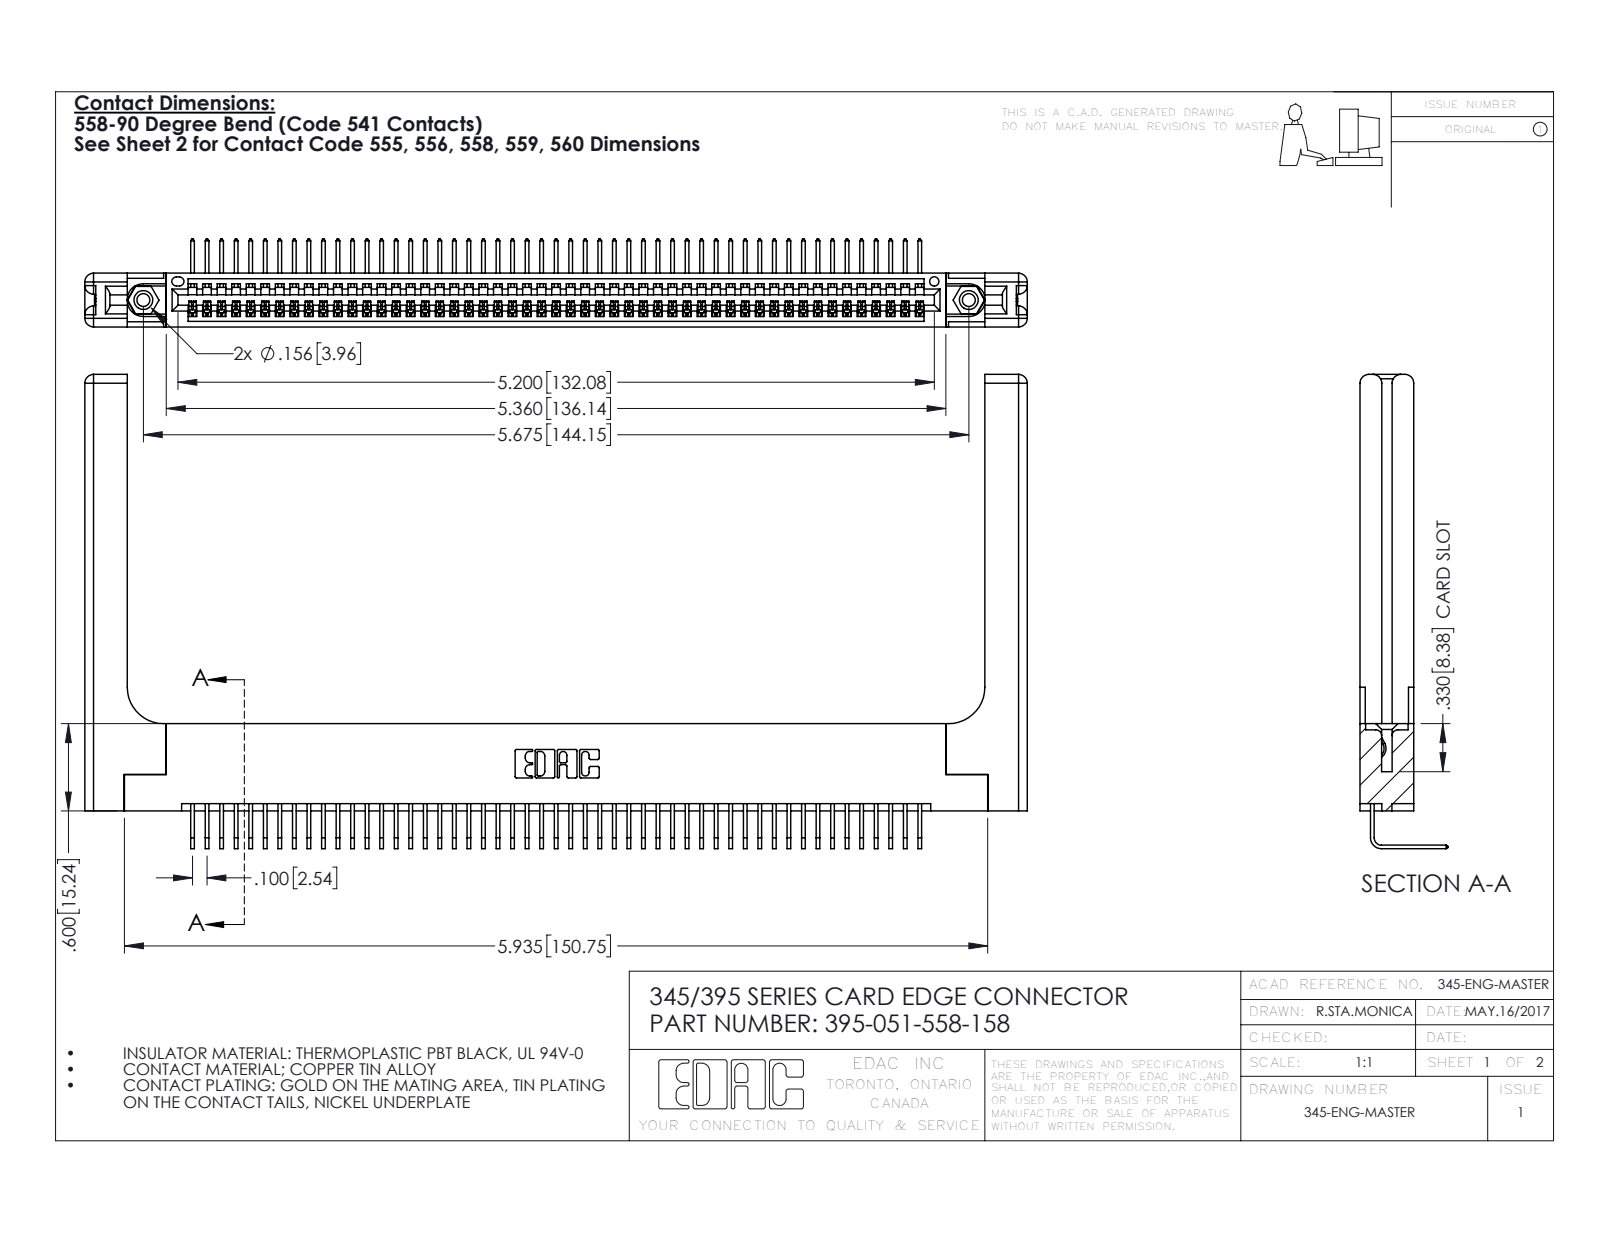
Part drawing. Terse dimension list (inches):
name: 395-051-558-158; 345-250-001_345-250-001-102; 345 Part_Flush Mounting Lugs - 0.156 Dia-TH; 345-292-001_558 Tail - 2 (+1 more)
written by: SolidWorks 2016 (CONFIG_CONTROL_DESIGN)
unit: in
bodies: 56 solids, 3442 faces (2370 planar, 1012 cylindrical, 60 other)
size: 6.479 × 3.259 × 0.605
volume: 1.488 in³; area: 42.66 in²
holes: 2× ⌀0.089, 2× ⌀0.125, 2× ⌀0.156, 1× ⌀0.064
bosses: 2× ⌀0.155
rounds: 102× R0.006, 22× R0.01, 16× R0.06, 6× R0.007, 6× R0.031, 3× R0.026, 2× R0.03, 2× R0.031
face distances: 0.072, 0.37, 0.298, 0.2, 0.098, 0.272, 0.025, 0.225, 0.148, 0.15
hole spacings: 0.27, 5.439, 5.675
